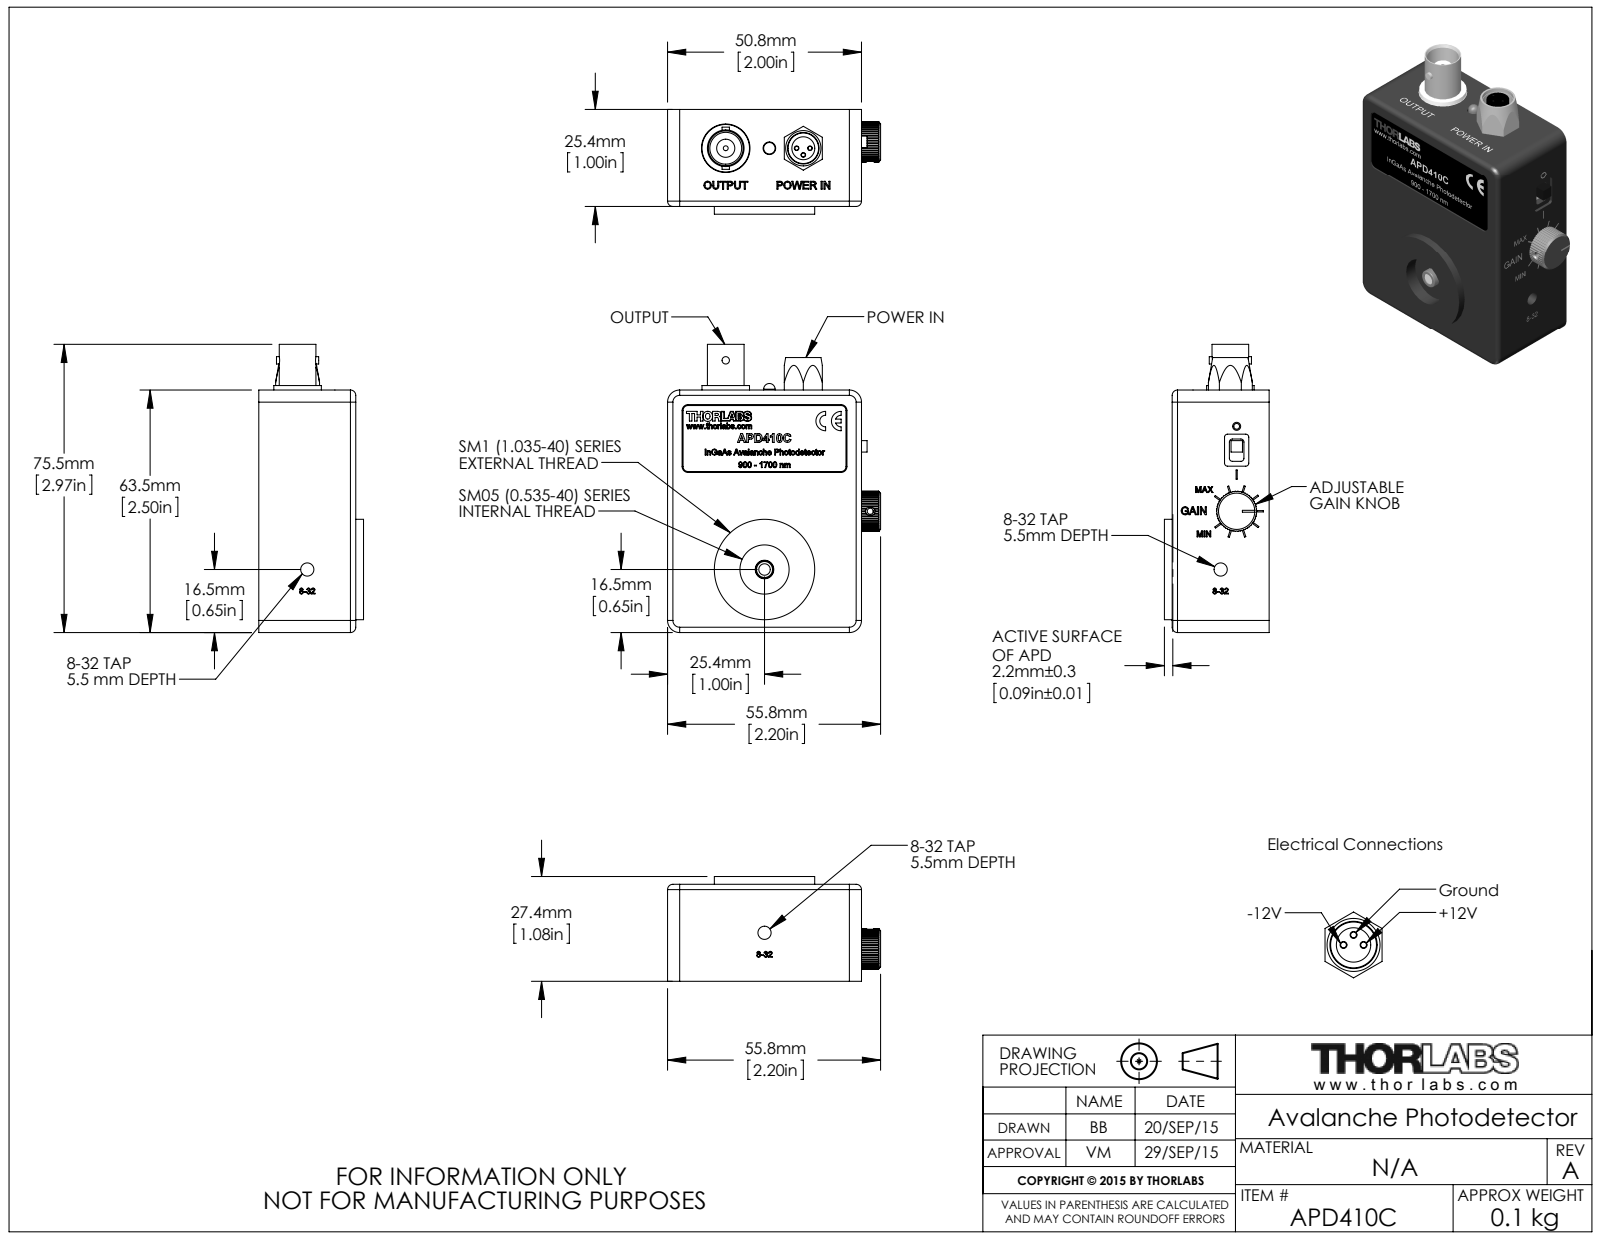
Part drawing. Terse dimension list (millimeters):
name: MTN005414
written by: SolidWorks 2014 (AUTOMOTIVE_DESIGN)
unit: mm
bodies: 0 solids, 2427 faces (1221 planar, 436 cylindrical, 770 other)
size: 75.46 × 55.8 × 27.43
holes: 9× ⌀1.6, 6× ⌀0.51, 4× ⌀2.4, 2× ⌀0.45, 2× ⌀2.5, 2× ⌀3.45, 1× ⌀1.27, 1× ⌀1.32, 1× ⌀2.1, 1× ⌀3, 1× ⌀3.3, 1× ⌀3.5
bosses: 5× ⌀1, 4× ⌀3.8, 4× ⌀2, 2× ⌀1.64, 2× ⌀1.6, 2× ⌀1.3, 1× ⌀26.29, 1× ⌀12.45
rounds: 53× R0.3, 19× R3.17, 14× R3.3, 8× R0.79, 8× R2.41, 6× R0.5, 6× R1.91, 5× R0.2
face distances: 1.59, 2.54, 0.4, 23.75, 22.16, 25.4, 23.81, 1.65, 25, 23.41
hole spacings: 41.17, 4.41, 51.14, 65.51, 2.49, 43.46, 1.27, 2
